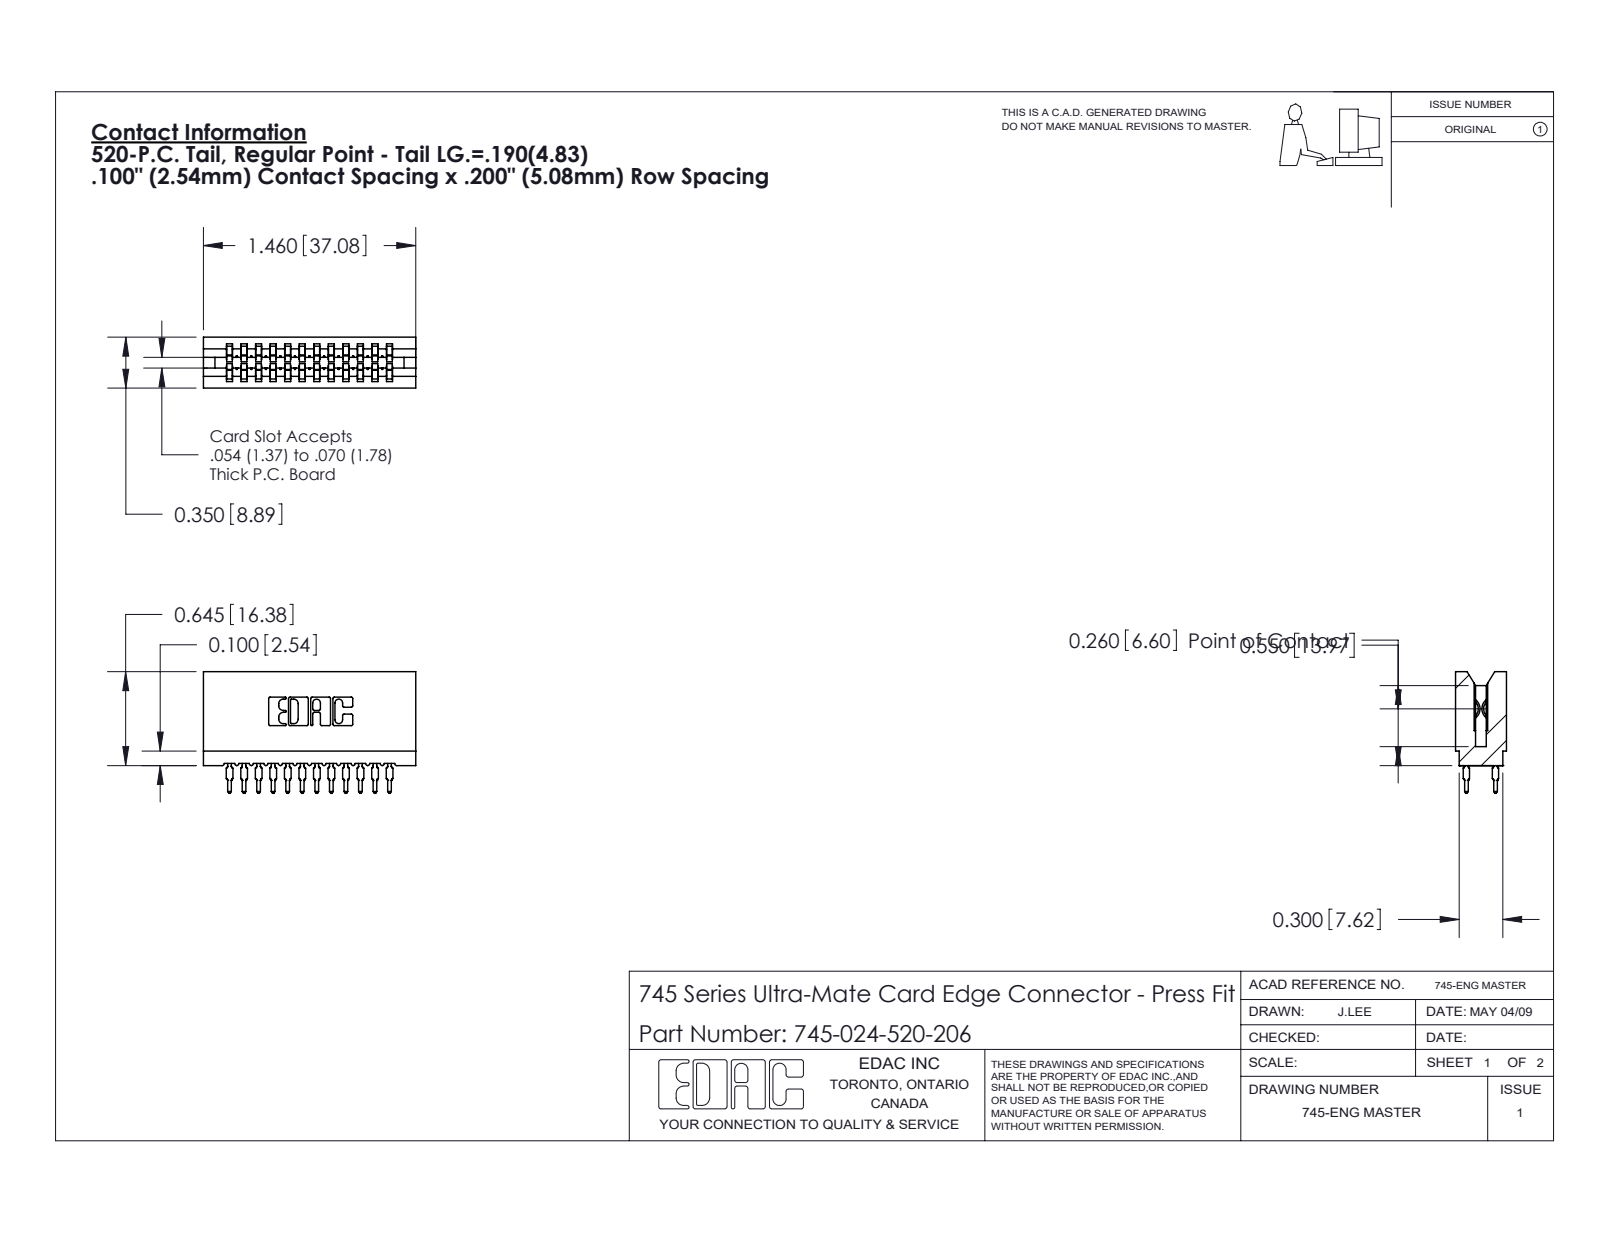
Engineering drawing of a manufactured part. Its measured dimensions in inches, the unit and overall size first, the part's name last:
Units: inches
Overall size (bounding box): 1.46 × 0.836 × 0.35
Partial cylindrical surfaces — rounded edges, fillets, slot ends (radius × count): R0.021 ×48, R0.015 ×24, R0.01 ×22, R0.005 ×8, R0.011 ×8, R0.007 ×6, R0.031 ×6, R0.026 ×3
Main face-to-face distances: 0.2, 0.1, 0.3, 0.4, 0.5, 0.058, 0.6, 0.042, 0.35, 0.358
Volume: 0.212 in³ · Surface area: 9.755 in²
Bodies: 25 solids, 2244 faces (1160 planar, 460 cylindrical, 624 other)
Part name (STEP PRODUCT): 745-292-001_520; 745-024-520-206; 745 Part_Insulator Option - 06
STEP written by: SolidWorks 2020 (CONFIG_CONTROL_DESIGN)
